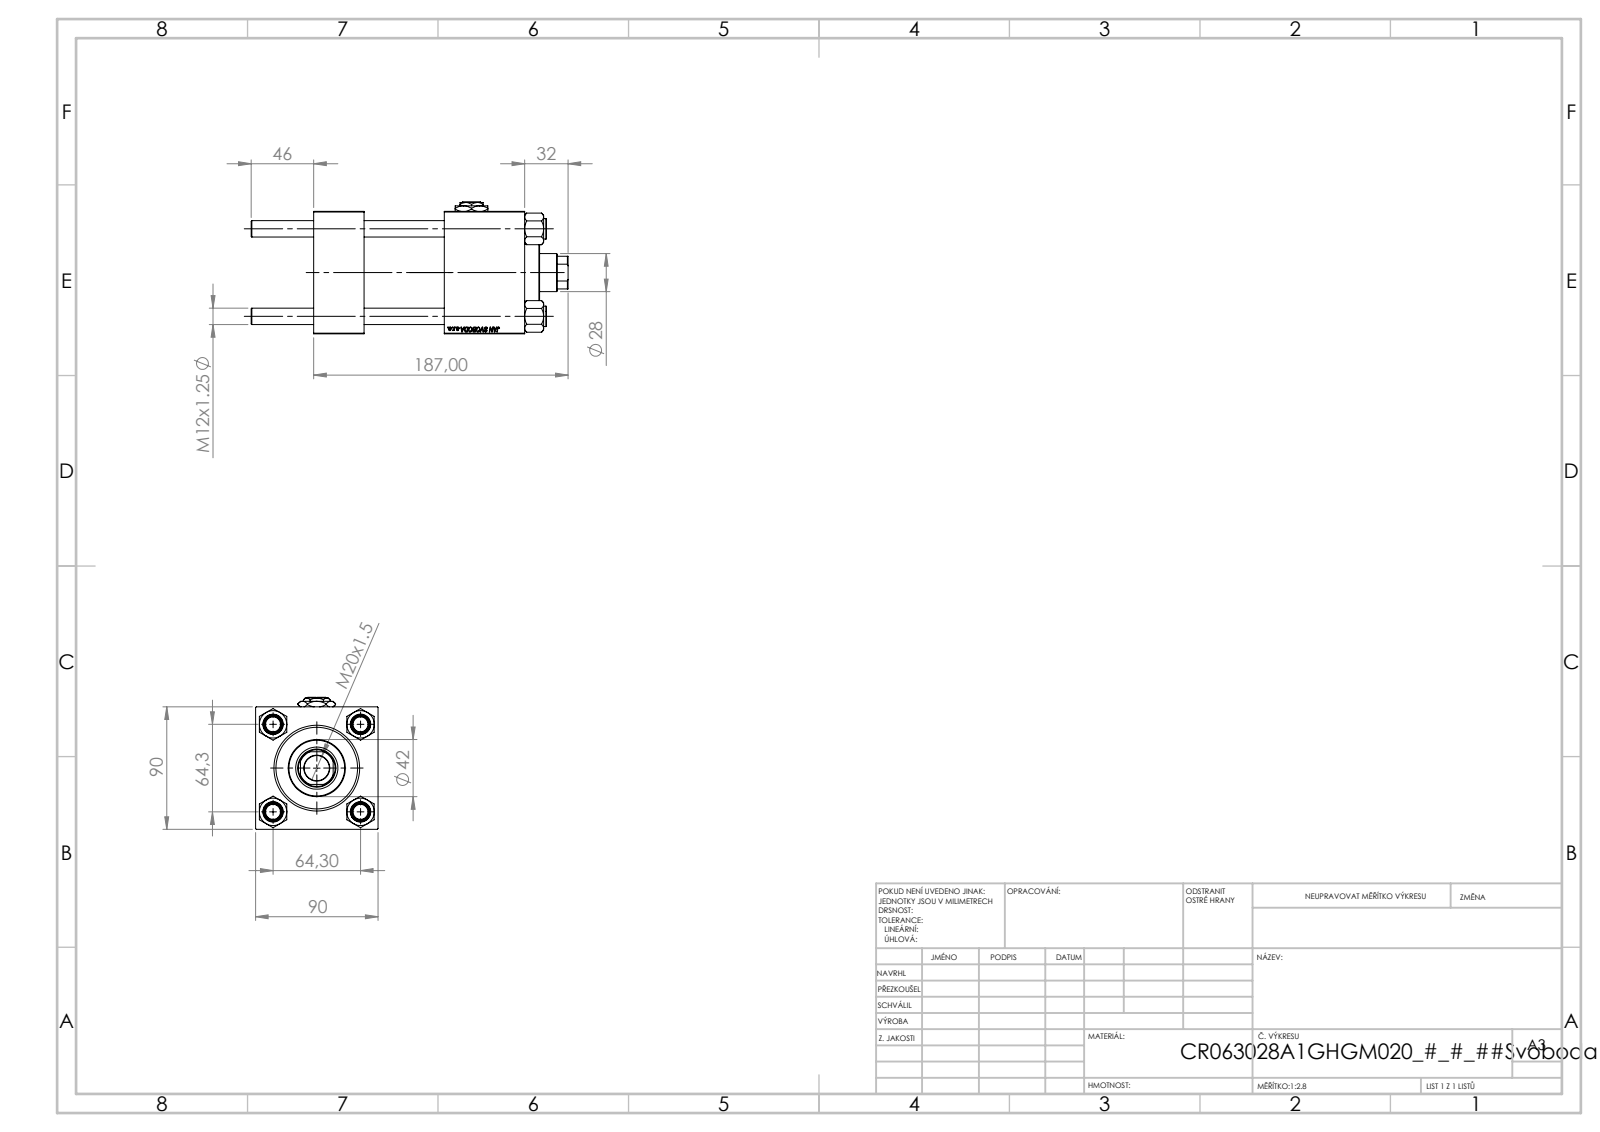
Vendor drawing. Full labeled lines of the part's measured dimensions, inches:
Part name (STEP PRODUCT): CR025_012_A_0_G_A_G_M_020_+#_##_TYCINKA; V215CR_BODY_A; NUT_M5; V215CR_VCP (+2 more)
STEP written by: SolidWorks 2019 (CONFIG_CONTROL_DESIGN)
Units: inches
Bodies: 12 solids, 1181 faces (543 planar, 82 cylindrical, 556 other)
Overall size (bounding box): 9.173 × 3.819 × 3.543
Volume: 59.61 in³ · Surface area: 306 in²
Round holes (diameter × count): ⌀0.472 ×4, ⌀0.276 ×2, ⌀0.825 ×2, ⌀1.181 ×2, ⌀0.728 ×1, ⌀1.102 ×1, ⌀1.22 ×1, ⌀1.969 ×1, ⌀2.362 ×1, ⌀2.48 ×1
Round bosses / shafts (diameter × count): ⌀0.591 ×4, ⌀2.717 ×1, ⌀1.654 ×1
Partial cylindrical surfaces — rounded edges, fillets, slot ends (radius × count): R0.531 ×1
Main face-to-face distances: 3.543, 2.323, 1.457, 6.102, 4.646, 3.78, 4.972, 3.516, 1.193, 1.13
Hole centre spacings: 1.79, 2.531, 3.58, 3.839
